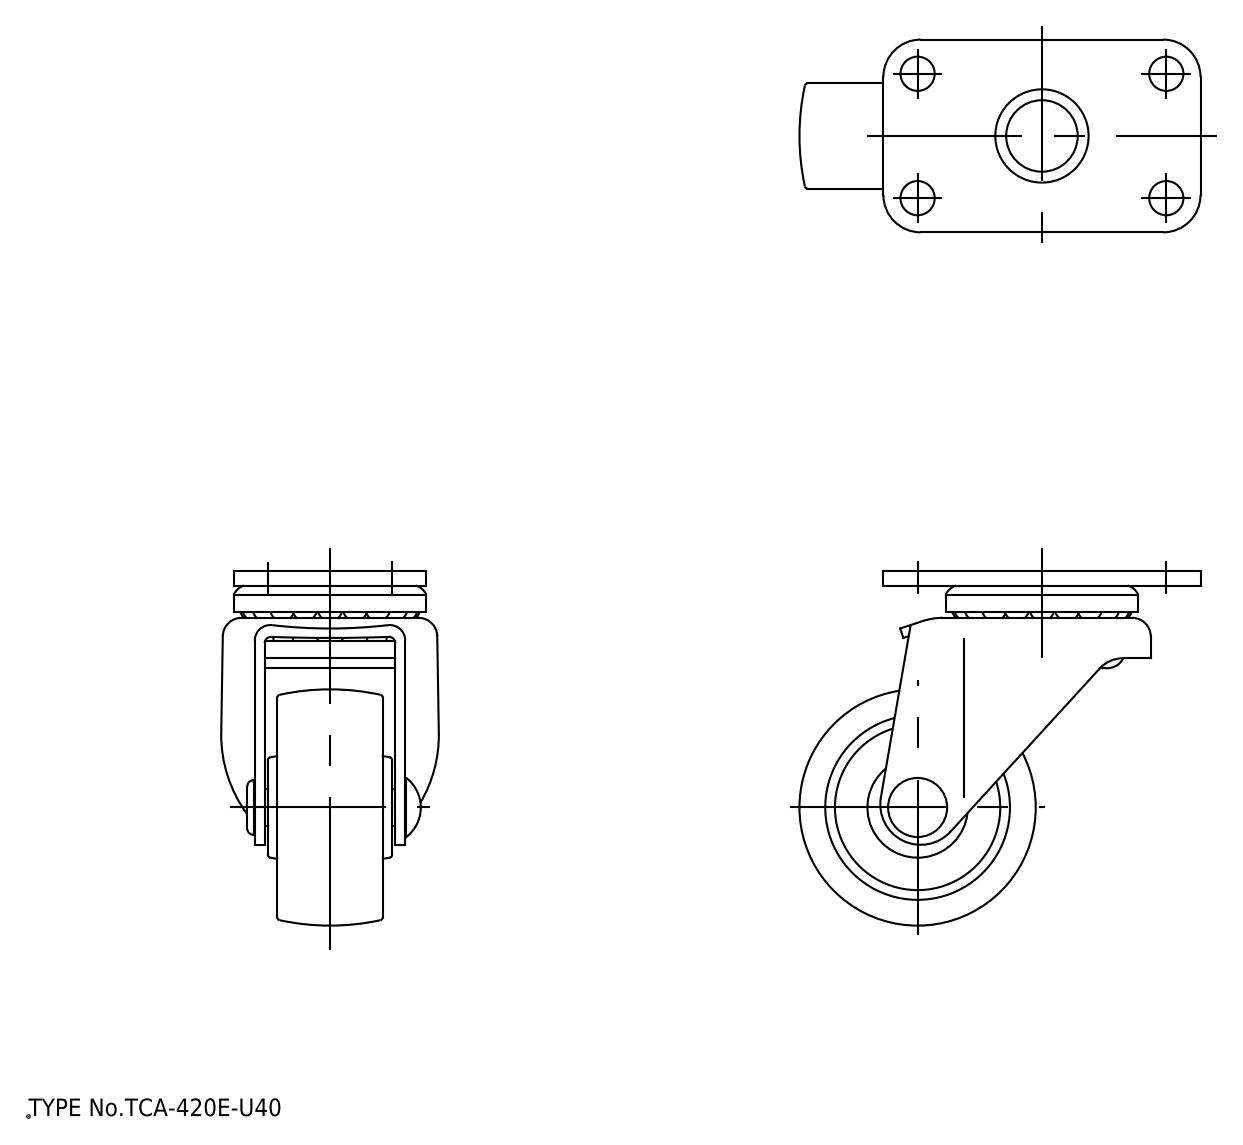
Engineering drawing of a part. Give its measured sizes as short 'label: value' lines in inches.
name: mounting plate; main shaft; axle; wheel
written by: spGate 19.8.4 (****-****-****-****) (AUTOMOTIVE_DESIGN)
unit: in
bodies: 5 solids, 193 faces (52 planar, 55 cylindrical, 86 other)
size: 2.539 × 2.244 × 1.378
volume: 1.667 in³; area: 29.01 in²
holes: 4× ⌀0.217, 1× ⌀0.236, 1× ⌀0.24, 1× ⌀0.422, 1× ⌀0.453, 1× ⌀0.591
bosses: 1× ⌀1.22, 1× ⌀1.024, 1× ⌀0.374
rounds: 5× R0.055, 4× R0.118, 4× R0.236, 3× R0.197, 1× R0.256, 1× R0.394, 1× R0.626, 1× R0.689
face distances: 0.091, 0.063, 0.295, 0.531, 0.358, 0.594, 0.89, 0.276, 0.22, 0.311
hole spacings: 0.88, 0.787, 1.575, 1.761
